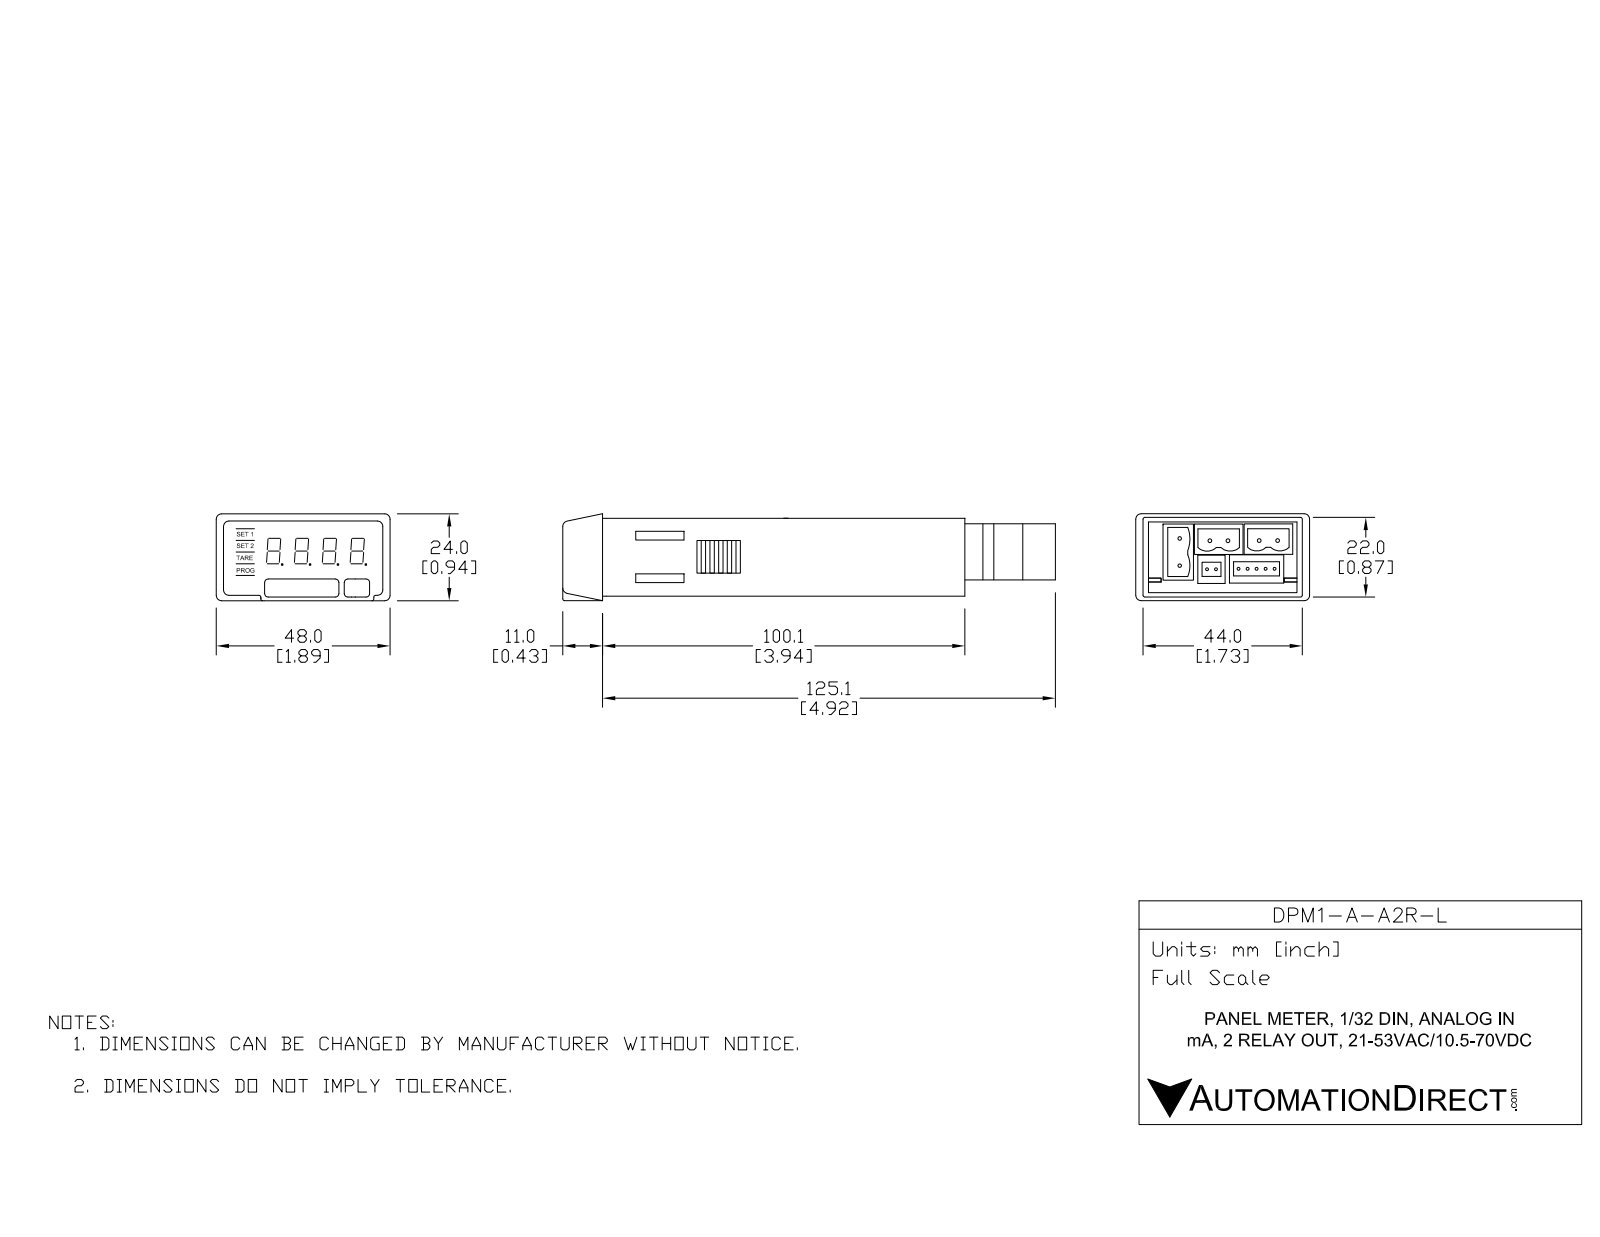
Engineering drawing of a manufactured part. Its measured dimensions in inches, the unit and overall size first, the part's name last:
Units: inches
Overall size (bounding box): 5.354 × 1.89 × 0.98
Round holes (diameter × count): ⌀0.039 ×7, ⌀0.079 ×7, ⌀0.078 ×6, ⌀0.118 ×6, ⌀0.152 ×6
Partial cylindrical surfaces — rounded edges, fillets, slot ends (radius × count): R0.012 ×14, R0.014 ×14, R0.02 ×14, R0.07 ×7, R0.072 ×7, R0.121 ×6, R0.039 ×4, R0.025 ×2
Main face-to-face distances: 0.059, 0.807, 0.866, 0.748, 1.673, 1.732, 1.614, 0.051, 0.433, 4.315
Hole centre spacings: 0.54, 0.138, 0.197, 0.197, 0.201, 0.201, 0.276, 0.286
Volume: 2.573 in³ · Surface area: 60.7 in²
Bodies: 6 solids, 1467 faces (1124 planar, 167 cylindrical, 176 other)
Part name (STEP PRODUCT): DPM1-A-A2R-L
STEP written by: SolidWorks 2017 (AUTOMOTIVE_DESIGN)
